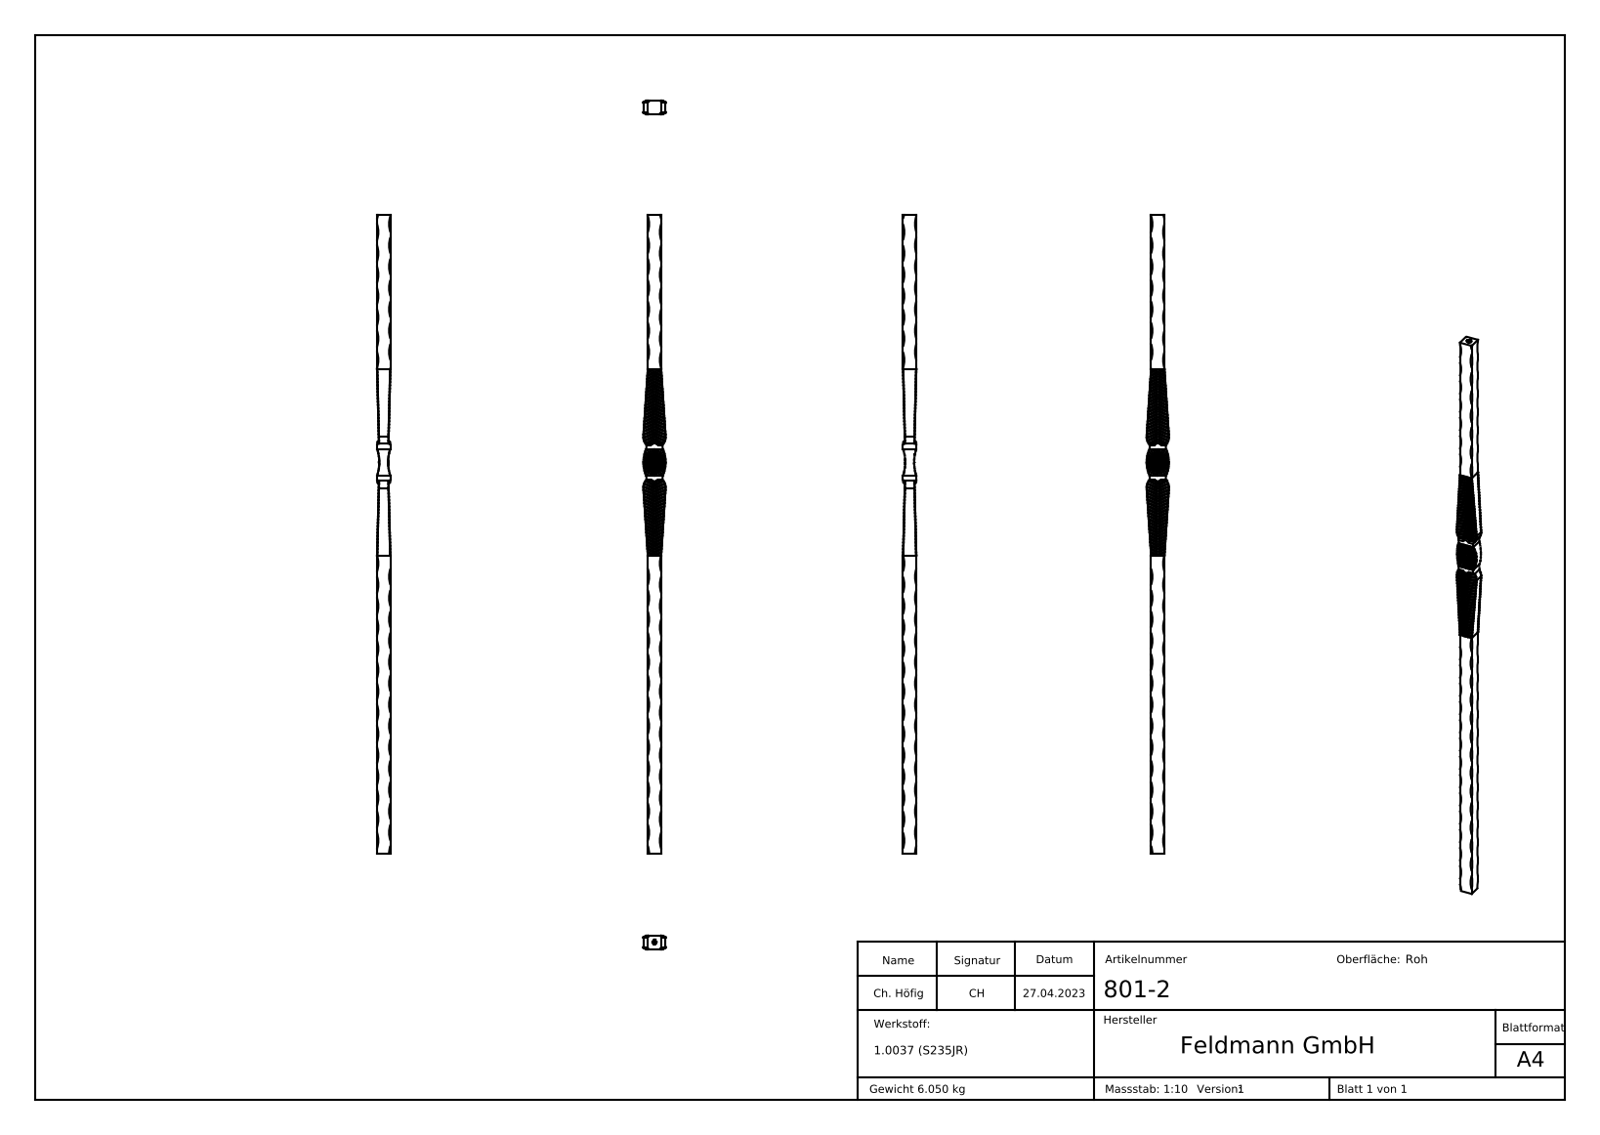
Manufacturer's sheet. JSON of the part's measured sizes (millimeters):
{"part_name": "801-2", "step_written_by": "SolidWorks 2018 (CONFIG_CONTROL_DESIGN)", "units": "millimeters", "bodies": {"solids": 1, "faces": 1210, "planar": 460, "cylindrical": 474, "other": 276}, "overall_size": [1200, 42, 25], "volume_mm3": 775682, "surface_area_mm2": 128126, "partial_cylinders_radius": [[61.92, 192], [68.06, 192], [3, 4], [10.03, 4], [20, 4], [62.97, 2], [80.12, 2], [80.62, 2]], "face_to_face_distances": [25, 0.5, 15.75, 16.25, 48.39, 15.25, 1200, 10, 60, 700]}
